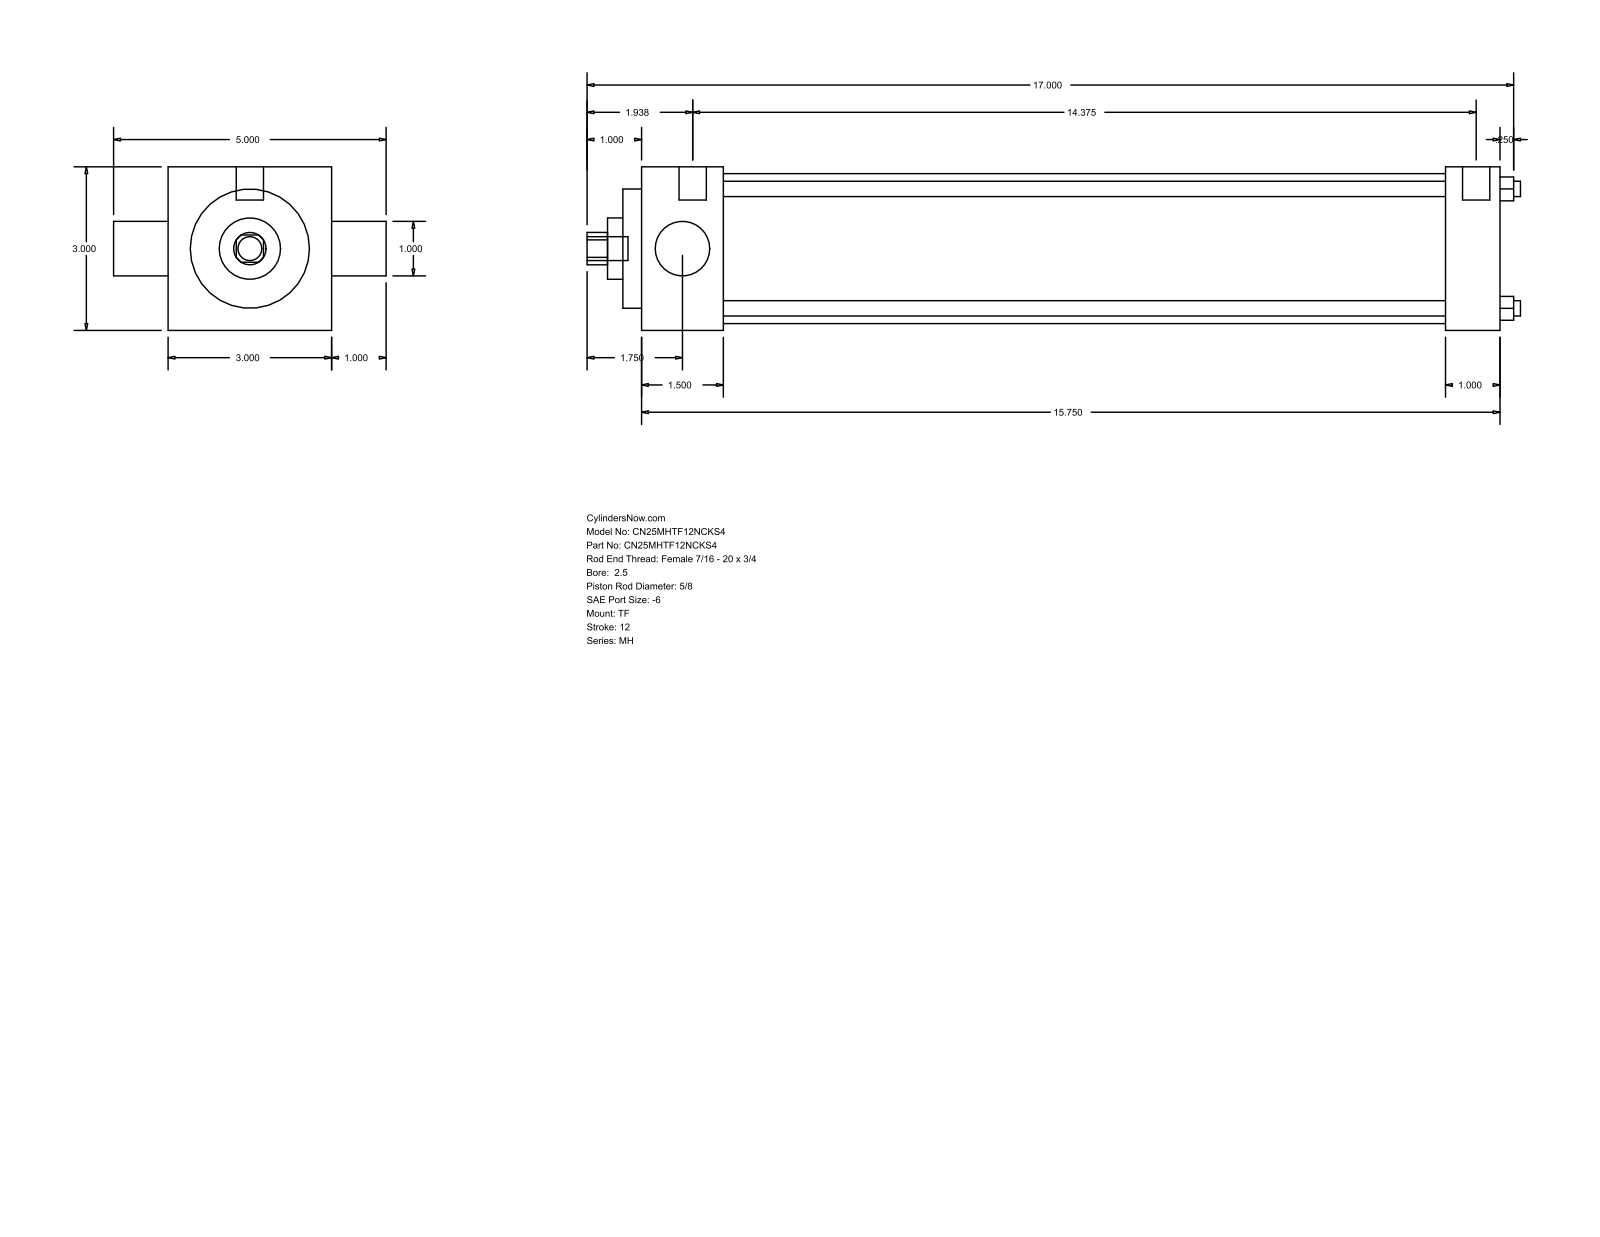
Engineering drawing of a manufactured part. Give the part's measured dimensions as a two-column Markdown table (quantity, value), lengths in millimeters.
| quantity | value |
| --- | --- |
| part name | MH_TF__0250_0.625 |
| STEP written by | GSSL Pune (CONFIG_CONTROL_DESIGN) |
| units | millimeters |
| bodies | 0 solids, 86 faces (61 planar, 25 cylindrical, 0 other) |
| overall size | 434.98 × 127 × 76.2 |
| round holes (diameter × count) | 7.14 × 4, 15.88 × 1, 25.4 × 1, 28.57 × 1, 55.55 × 1, 69.85 × 1 |
| round bosses / shafts (diameter × count) | 5.56 × 3, 12.7 × 2, 11.11 × 1 |
| partial cylindrical surfaces (radius × count) | 7.54 × 1 |
| main face-to-face distances | 76.2, 400.05, 25.4, 38.1, 361.95, 374.65, 336.55, 8.73, 46.83, 383.38 |
| hole center spacings | 39.33, 55.62, 78.66 |
